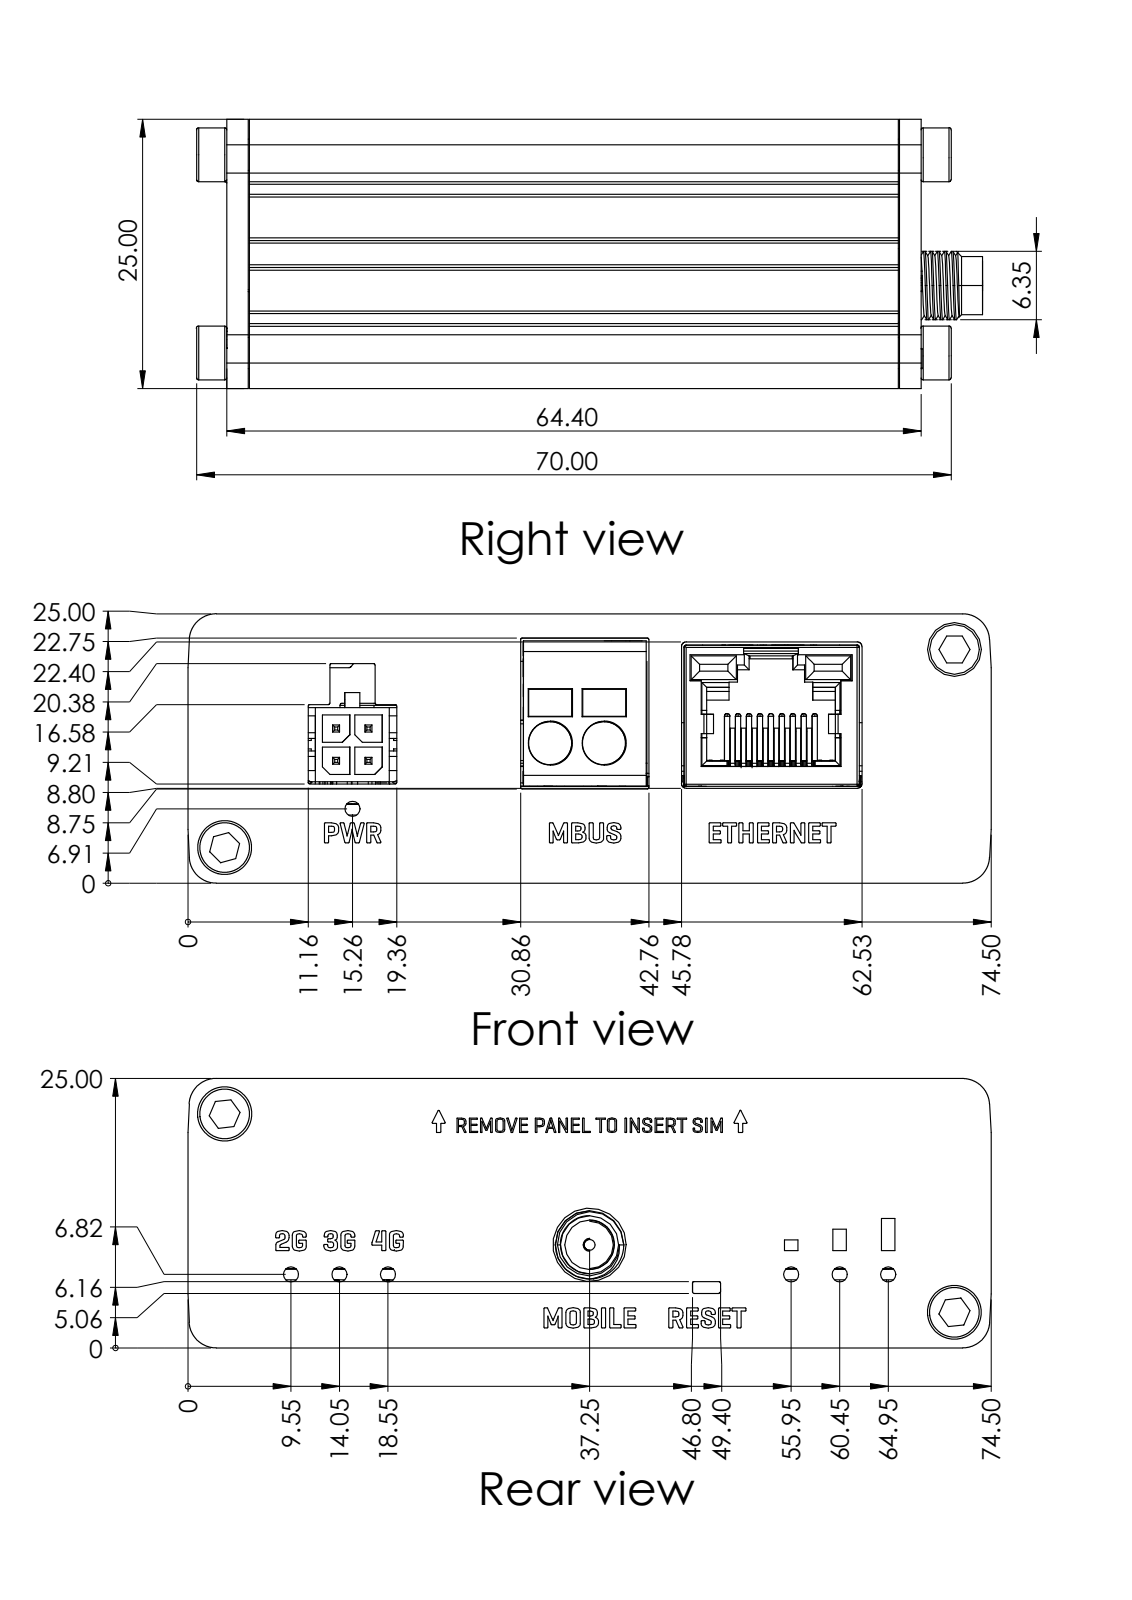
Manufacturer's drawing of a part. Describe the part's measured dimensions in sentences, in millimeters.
The part is named "O-ring(DIN 3771); TRB143_Rear_Panel_T143DRP002_v2; TRB143_T14XDHS002_T143DFP002_T143DRP002; Savisriegis 2.9x6.5 (+4 more)". Its 3-D file was written by "SolidWorks 2022 (AUTOMOTIVE_DESIGN)". It is 15 solids with 19277 faces: 12702 planar, 4060 cylindrical and 2515 other. Overall it measures 74.5 by 72.89 by 25 millimeters. Its volume is 36 878 cubic millimeters and its surface area 66 349 square millimeters. Round holes: 7 of diameter 1, 7 of diameter 1.4, 2 of diameter 0.2, 2 of diameter 0.58, 2 of diameter 1.5, 2 of diameter 3.3, 2 of diameter 4, 1 of diameter 0.25, 1 of diameter 0.33, 1 of diameter 0.55, 1 of diameter 3, 1 of diameter 4.4. Round bosses or shafts: 45 of diameter 1, 12 of diameter 0.9, 3 of diameter 8, 3 of diameter 5, 2 of diameter 8.3, 2 of diameter 6.3, 2 of diameter 3.25, 2 of diameter 2.9. Partial cylindrical surfaces (rounded edges, fillets, slot ends): 430 of radius 0.1, 124 of radius 0.25, 75 of radius 0.2, 61 of radius 0.15, 59 of radius 0.17, 54 of radius 0.5, 34 of radius 0.3, 24 of radius 0.25. The main face-to-face distances are 2, 9, 1.65, 22.75, 2.25, 13.75, 22.5, 24.75, 15.75, 4.5. The hole center spacings are 4.5, 46.4, 3.36, 3.7, 5.44, 5.95, 6.4, 7.11.
